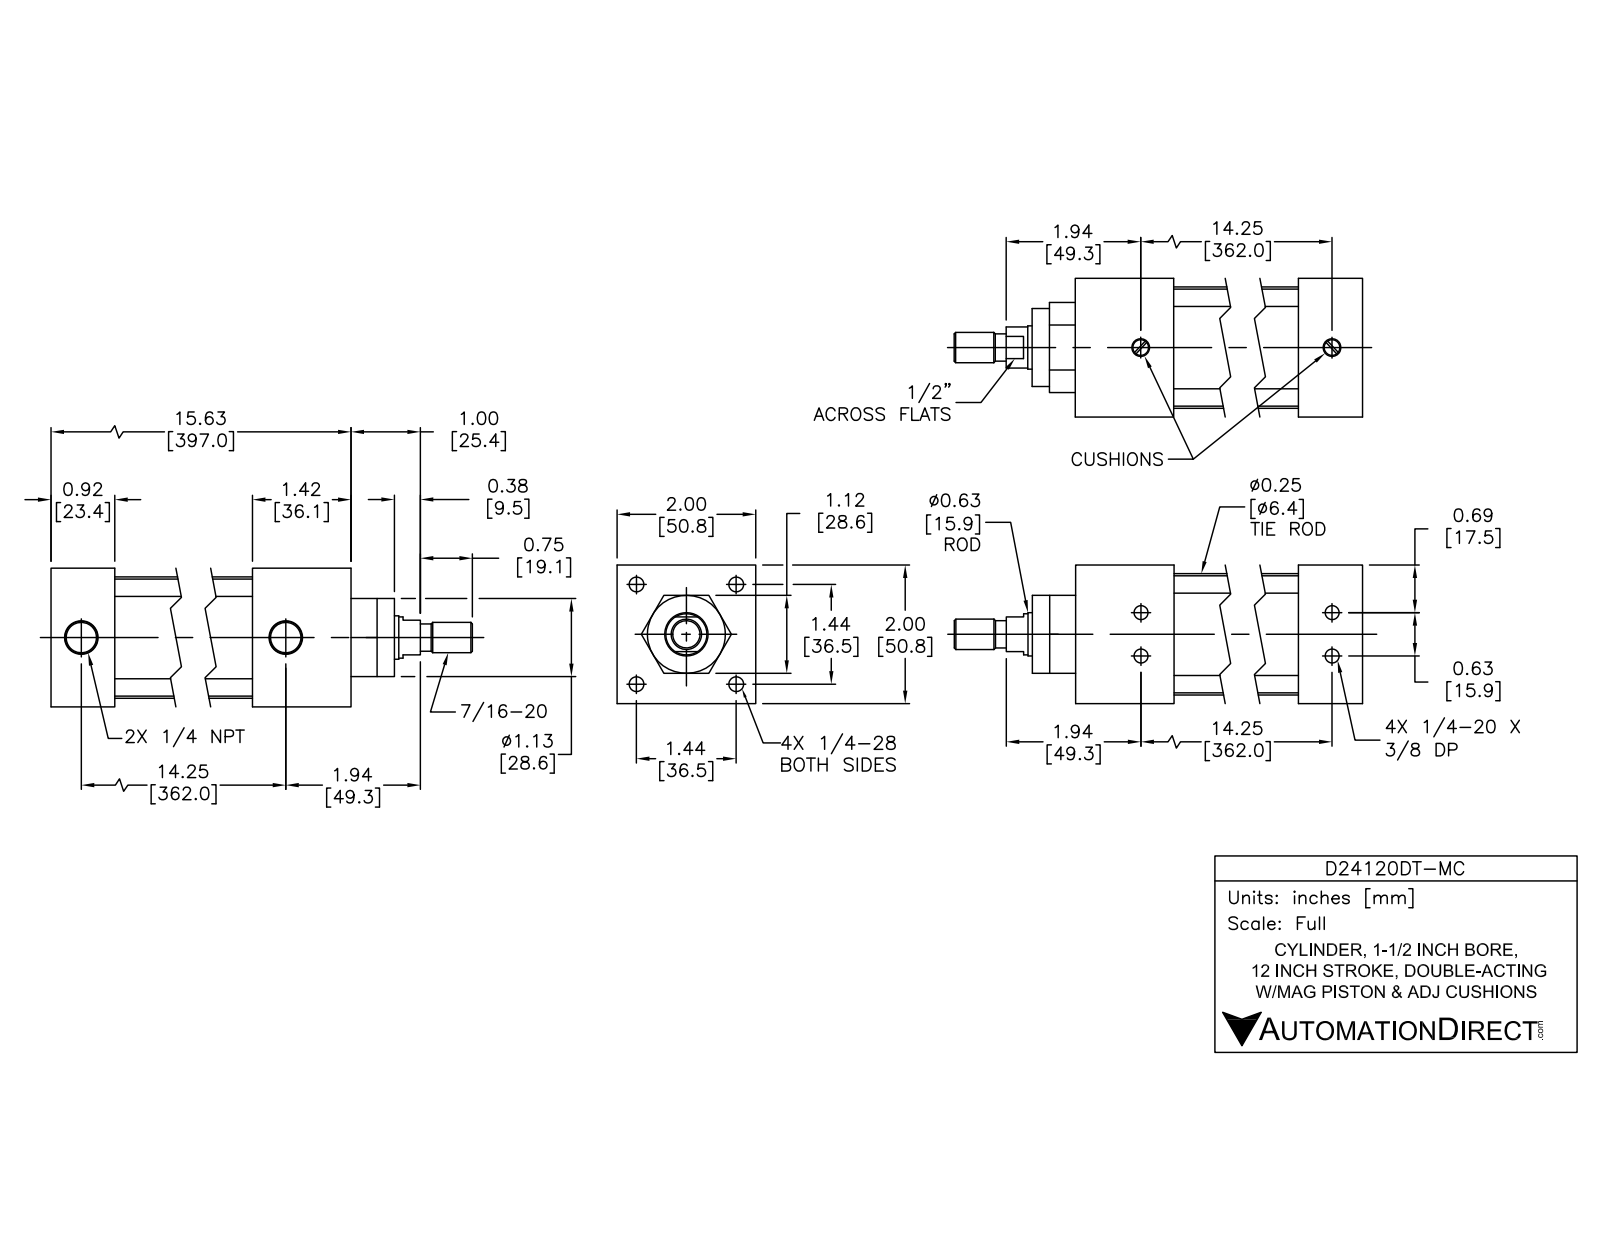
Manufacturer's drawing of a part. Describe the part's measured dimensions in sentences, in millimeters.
The part is named "D24120DT-M BODY; D24120DT-M PISTON; D24120DT-MC". Its 3-D file was written by "SolidWorks 2015 (AUTOMOTIVE_DESIGN)". It is 12 solids with 303 faces: 99 planar, 114 cylindrical and 90 other. Overall it measures 441.2 by 50.8 by 50.8 millimeters. Its volume is 423 600 cubic millimeters and its surface area 175 800 square millimeters. Round holes: 4 of diameter 5, 4 of diameter 5.4, 4 of diameter 7.1, 4 of diameter 10.3, 2 of diameter 7.5, 2 of diameter 12.1, 1 of diameter 15.9, 1 of diameter 16, 1 of diameter 38.1. Round bosses or shafts: 4 of diameter 9.9, 4 of diameter 6.4, 4 of diameter 5.6, 1 of diameter 44.5, 1 of diameter 38, 1 of diameter 28.5, 1 of diameter 15.8, 1 of diameter 15. Partial cylindrical surfaces (rounded edges, fillets, slot ends): 4 of radius 5.1. The main face-to-face distances are 50.8, 2, 335.3, 396.8, 36.1, 360.7, 373.4, 337.3, 23.4, 28.5. The hole center spacings are 362, 7.9, 8, 15.9, 25.8, 25.8, 36.4, 36.4.
